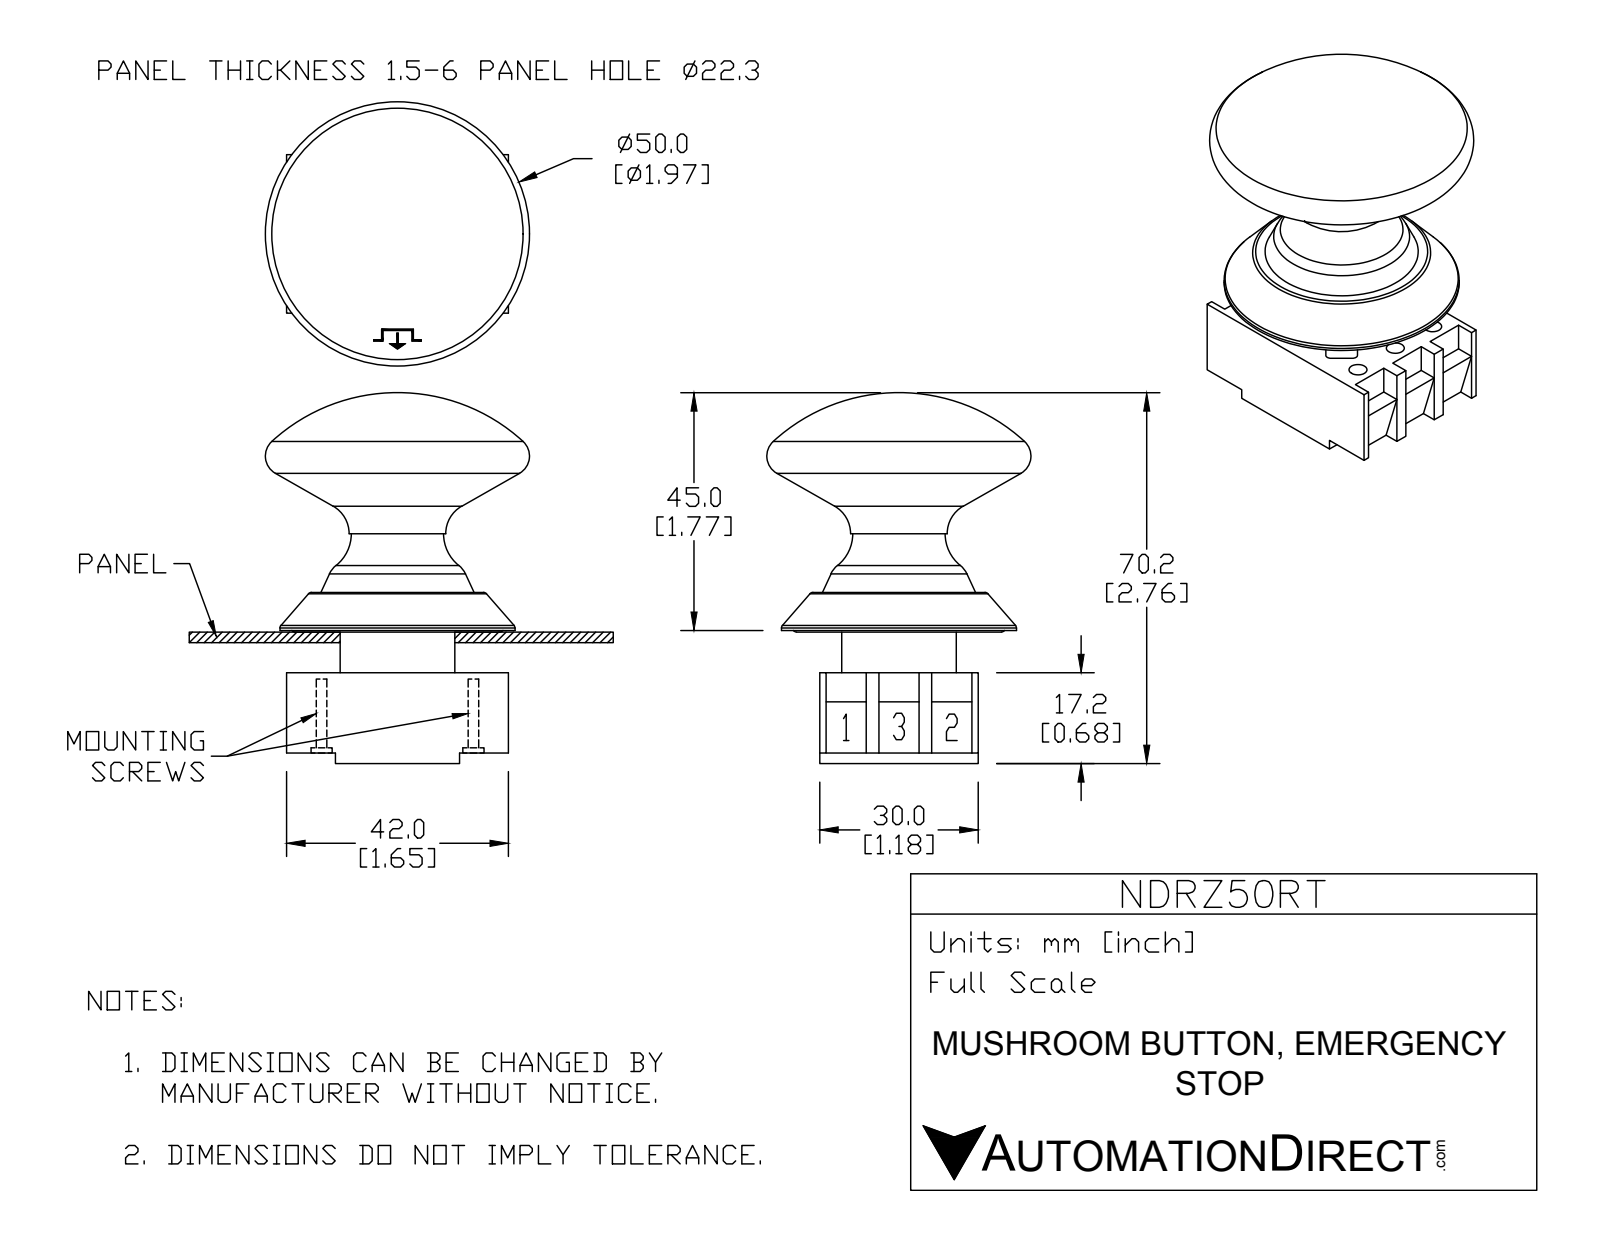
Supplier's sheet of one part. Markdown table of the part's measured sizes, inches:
| quantity | value |
| --- | --- |
| part name | NDRZ50RT |
| STEP written by | SolidWorks 2015 (AUTOMOTIVE_DESIGN) |
| units | inches |
| bodies | 7 solids, 222 faces (126 planar, 63 cylindrical, 33 other) |
| overall size | 2.764 × 1.969 × 1.969 |
| volume | 3.399 in³ |
| surface area | 33.49 in² |
| round holes (diameter × count) | 0.134 × 6, 0.197 × 6, 0.492 × 1 |
| round bosses / shafts (diameter × count) | 0.181 × 2, 0.157 × 2, 1.752 × 1, 0.854 × 1 |
| partial cylindrical surfaces (radius × count) | 0.039 × 8, 0.343 × 5, 0.433 × 1 |
| main face-to-face distances | 0.283, 0.598, 1.181, 0.315, 0.295, 0.303, 0.902, 0.394, 0.913, 1.197 |
| hole center spacings | 0.394, 0.69, 1.199, 1.132, 0.566, 0.787, 1.379 |
